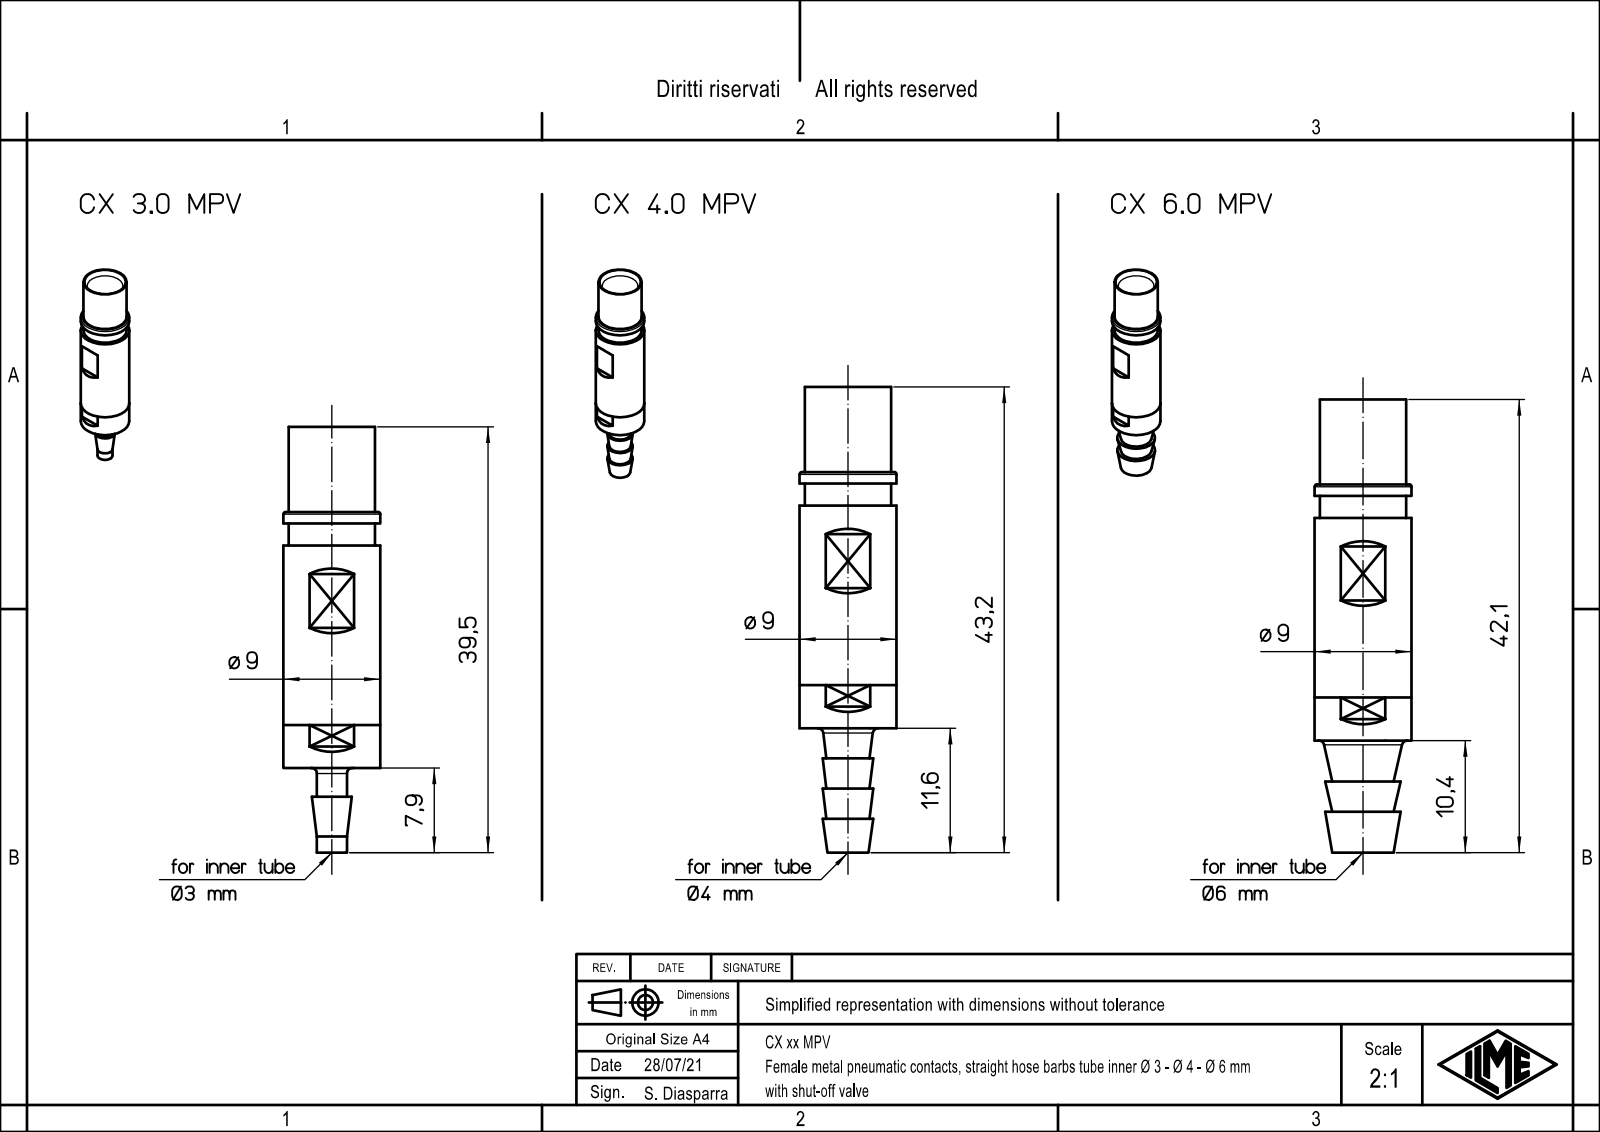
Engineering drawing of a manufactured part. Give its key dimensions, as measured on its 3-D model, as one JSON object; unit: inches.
{"part_name": "CX_3.0_MPV", "step_written_by": "Creo Elements/Direct Modeling 20.1B 02-Apr-2019 (C) Parametric Technology GmbH (AUTOMOTIVE_DESIGN)", "units": "inches", "bodies": {"solids": 1, "faces": 73, "planar": 33, "cylindrical": 22, "other": 18}, "overall_size": [1.555, 0.354, 0.354], "volume_in3": 0.097, "surface_area_in2": 2.26, "round_holes": [[0.079, 1], [0.26, 1]], "round_bosses_or_shafts": [[0.354, 1], [0.315, 1], [0.307, 1], [0.183, 1], [0.11, 1]], "face_to_face_distances": [0.146, 0.169, 0.024, 0.315, 0.894, 0.157, 0.736, 0.159, 0.734, 0.813]}
